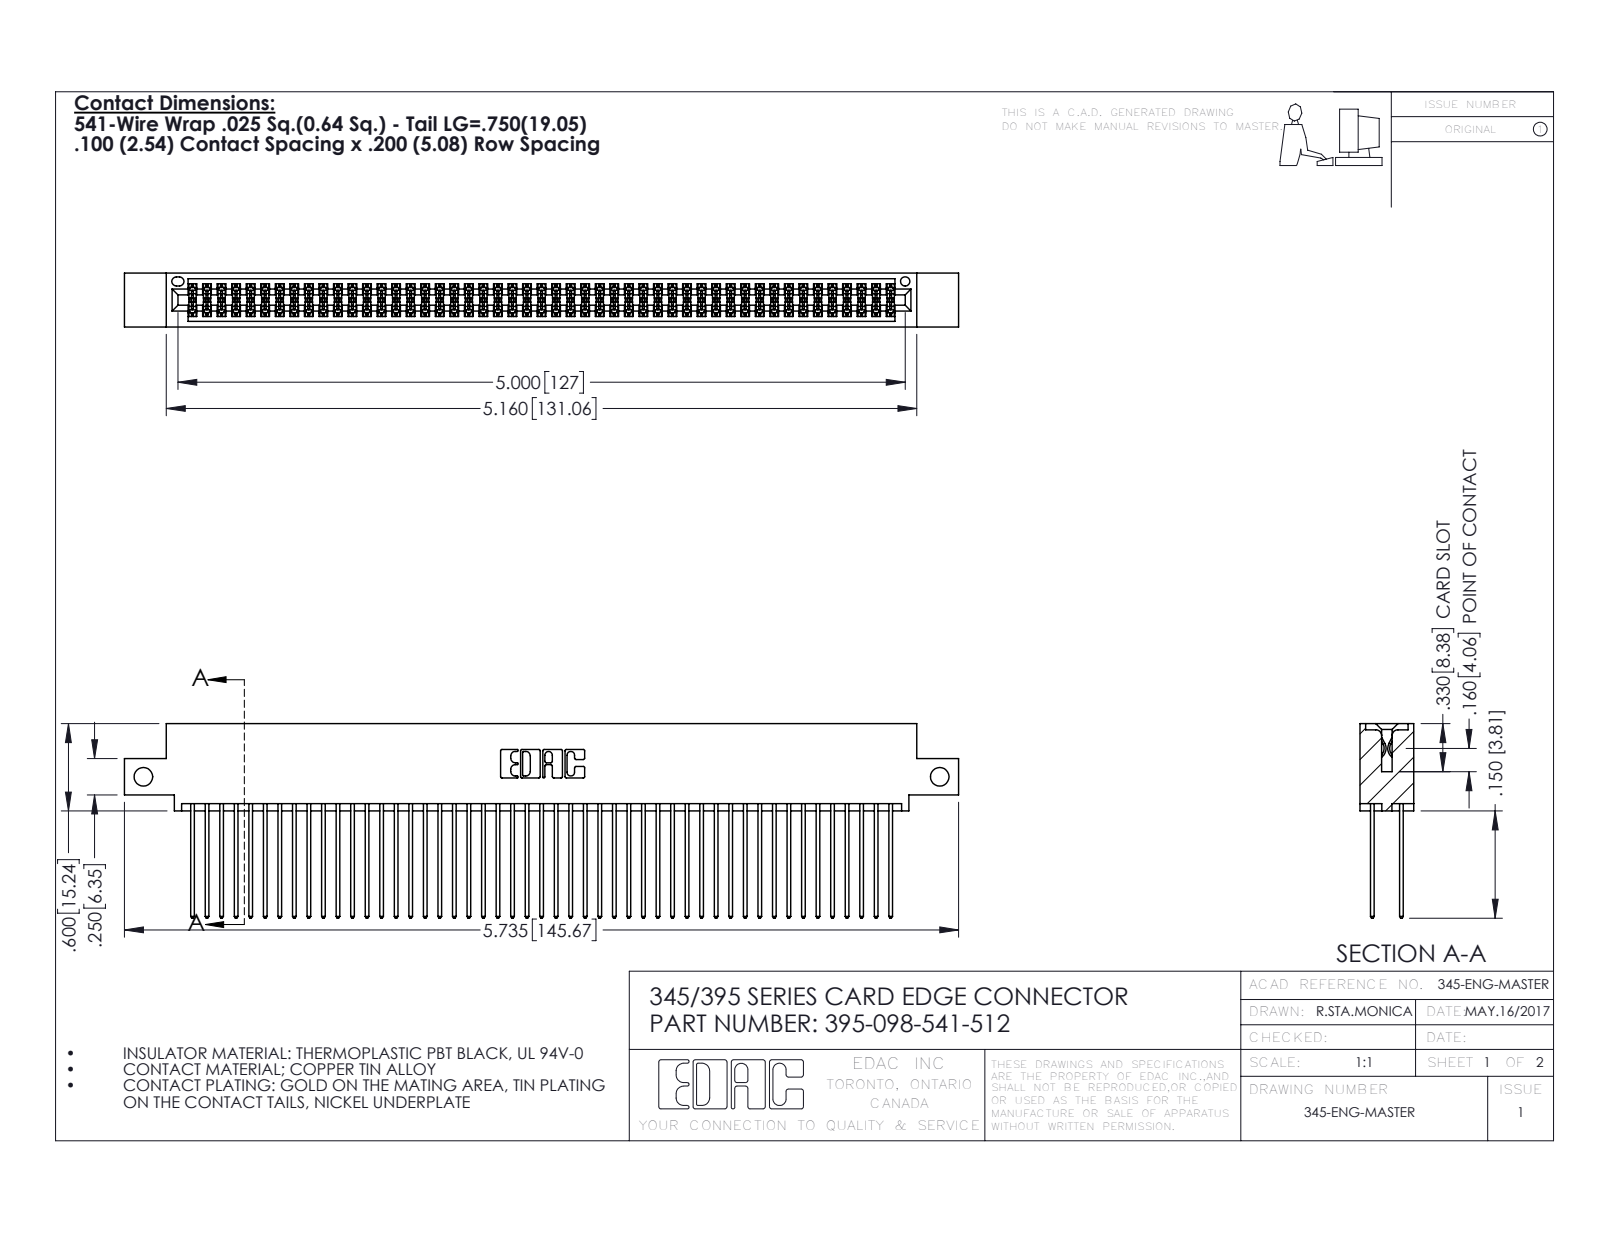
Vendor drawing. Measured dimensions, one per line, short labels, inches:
name: 345-292-001_345-293-141; 395-098-541-512; 345 Part_0.110 Offset - Side Mount
written by: SolidWorks 2016 (CONFIG_CONTROL_DESIGN)
unit: in
bodies: 99 solids, 5030 faces (3318 planar, 1712 cylindrical, 0 other)
size: 5.735 × 1.337 × 0.37
volume: 0.892 in³; area: 37.73 in²
holes: 2× ⌀0.128, 1× ⌀0.064
rounds: 147× R0.006, 98× R0.01, 22× R0.01, 6× R0.007, 6× R0.031, 3× R0.026, 2× R0.014, 2× R0.019
face distances: 0.072, 0.298, 0.2, 0.098, 0.272, 0.025, 0.225, 0.37, 0.175, 0.149
hole spacings: 5.475
